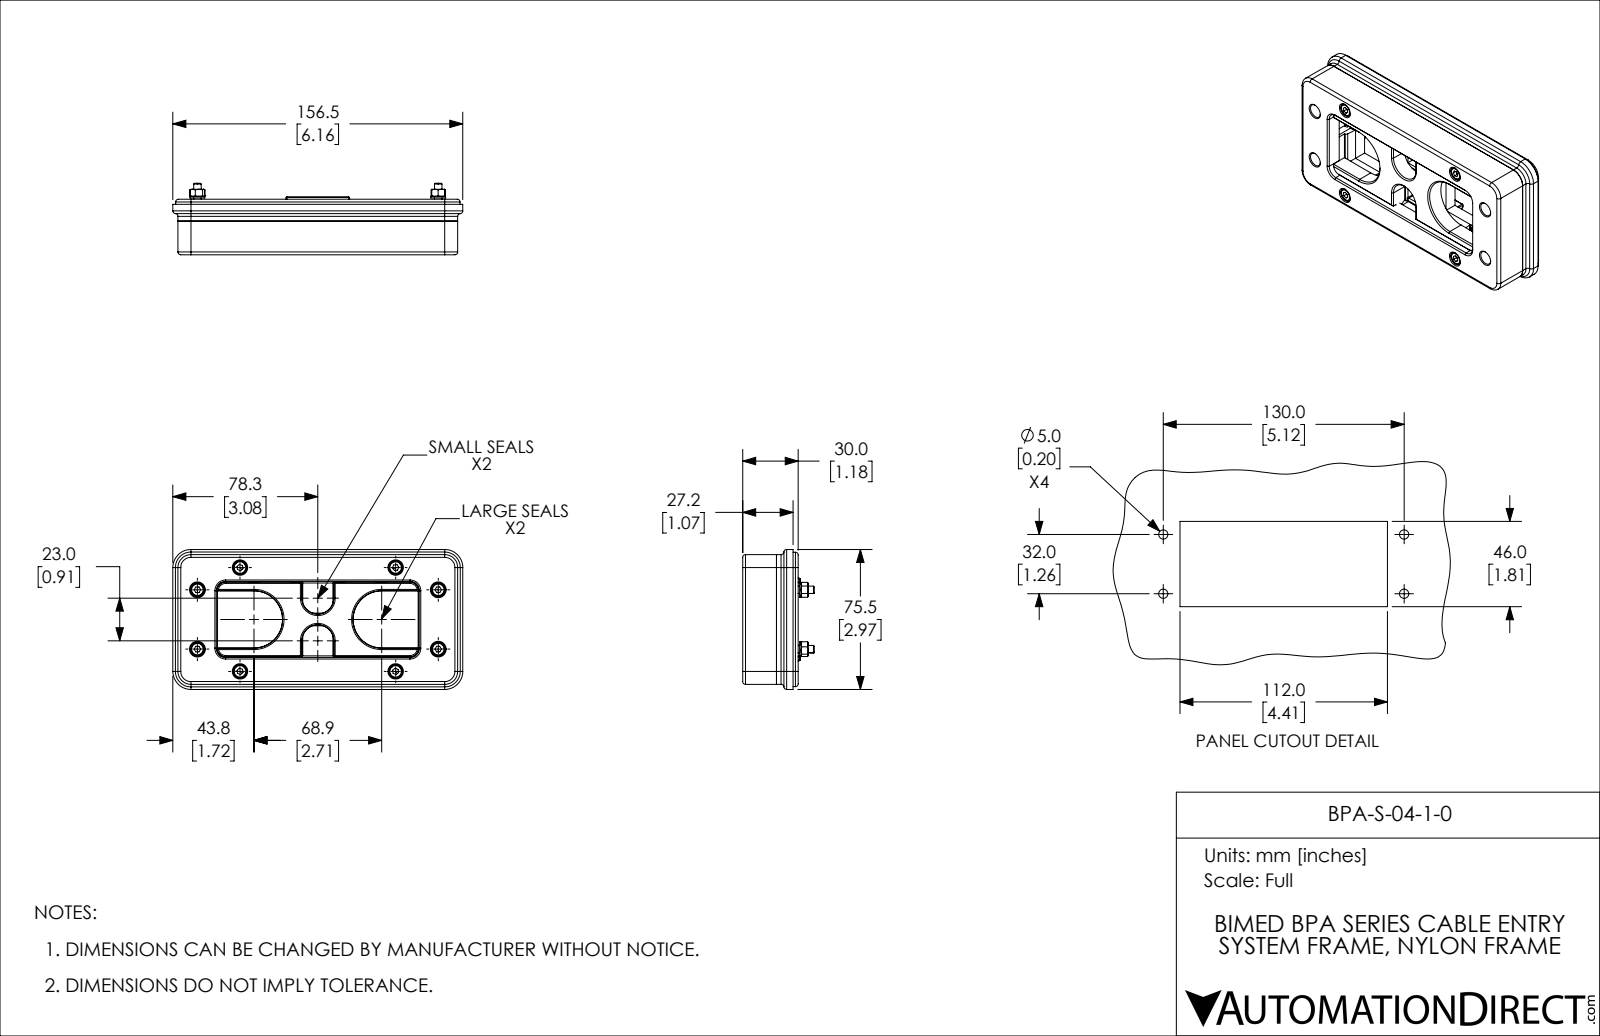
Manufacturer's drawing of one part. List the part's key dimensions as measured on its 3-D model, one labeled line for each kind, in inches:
Part name (STEP PRODUCT): BPA-S-04-1-0
STEP written by: SolidWorks 2021 (CONFIG_CONTROL_DESIGN)
Units: inches
Bodies: 29 solids, 1745 faces (865 planar, 522 cylindrical, 358 other)
Overall size (bounding box): 6.161 × 2.972 × 1.52
Volume: 11.05 in³ · Surface area: 146.5 in²
Round holes (diameter × count): ⌀0.128 ×8, ⌀0.177 ×8, ⌀0.169 ×4, ⌀0.197 ×4, ⌀0.287 ×4, ⌀0.295 ×4, ⌀0.315 ×4
Round bosses / shafts (diameter × count): ⌀0.276 ×8, ⌀0.157 ×8, ⌀0.319 ×4, ⌀0.315 ×4, ⌀0.272 ×4
Partial cylindrical surfaces — rounded edges, fillets, slot ends (radius × count): R0.02 ×51, R0.039 ×32, R0.059 ×20, R0.016 ×10, R0.03 ×4, R0.134 ×4, R0.138 ×4, R0.157 ×4
Main face-to-face distances: 0.089, 0.098, 2.667, 1.071, 0.74, 0.331, 0.118, 0.378, 0.138, 2.657
Hole centre spacings: 1.021, 1.955, 4.239, 4.555, 1.26, 2.205, 3.307, 3.975
